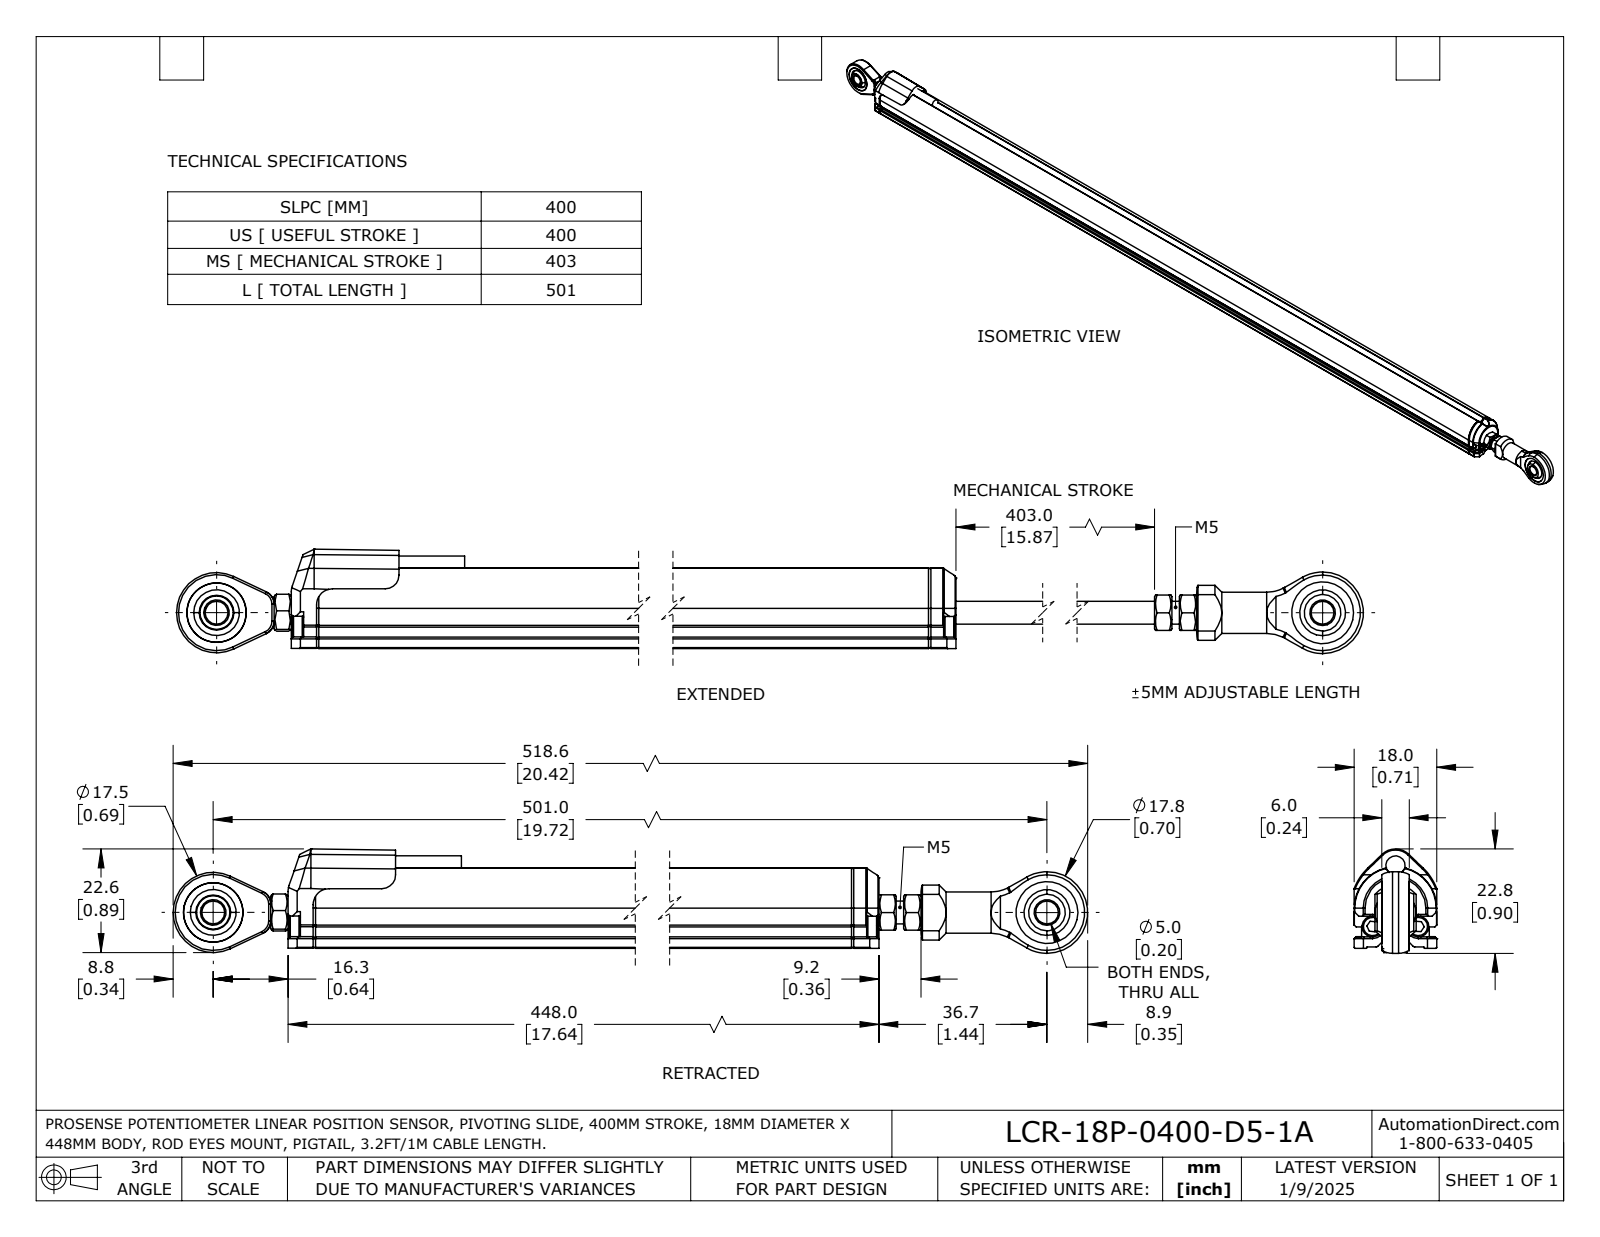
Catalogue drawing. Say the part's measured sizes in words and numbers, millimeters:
The part is named "LCR-18P-0400-D5-1A". Its 3-D file was written by "SolidWorks 2023 (AUTOMOTIVE_DESIGN)". It is 20 solids with 515 faces: 289 planar, 136 cylindrical and 90 other. Overall it measures 518.6 by 22.8 by 18 millimeters. Its volume is 123 100 cubic millimeters and its surface area 43 590 square millimeters. Round holes: 4 of diameter 5, 2 of diameter 2.6, 2 of diameter 2.6, 2 of diameter 10, 1 of diameter 5.4, 1 of diameter 6.9, 1 of diameter 13, 1 of diameter 13.5. Round bosses or shafts: 4 of diameter 4.6, 3 of diameter 2.9, 2 of diameter 1.5, 1 of diameter 9, 1 of diameter 4.2, 1 of diameter 2.9. Partial cylindrical surfaces (rounded edges, fillets, slot ends): 12 of radius 0.2, 10 of radius 0.1, 8 of radius 0.5, 6 of radius 0.3, 6 of radius 0.5, 4 of radius 0.4, 4 of radius 1, 4 of radius 1.1. The main face-to-face distances are 18, 1.6, 16.4, 1.8, 1.5, 2.2, 2.5, 0.7, 4.7, 4.4. The hole center spacings are 5.9, 10, 5.8, 5.9, 501.
